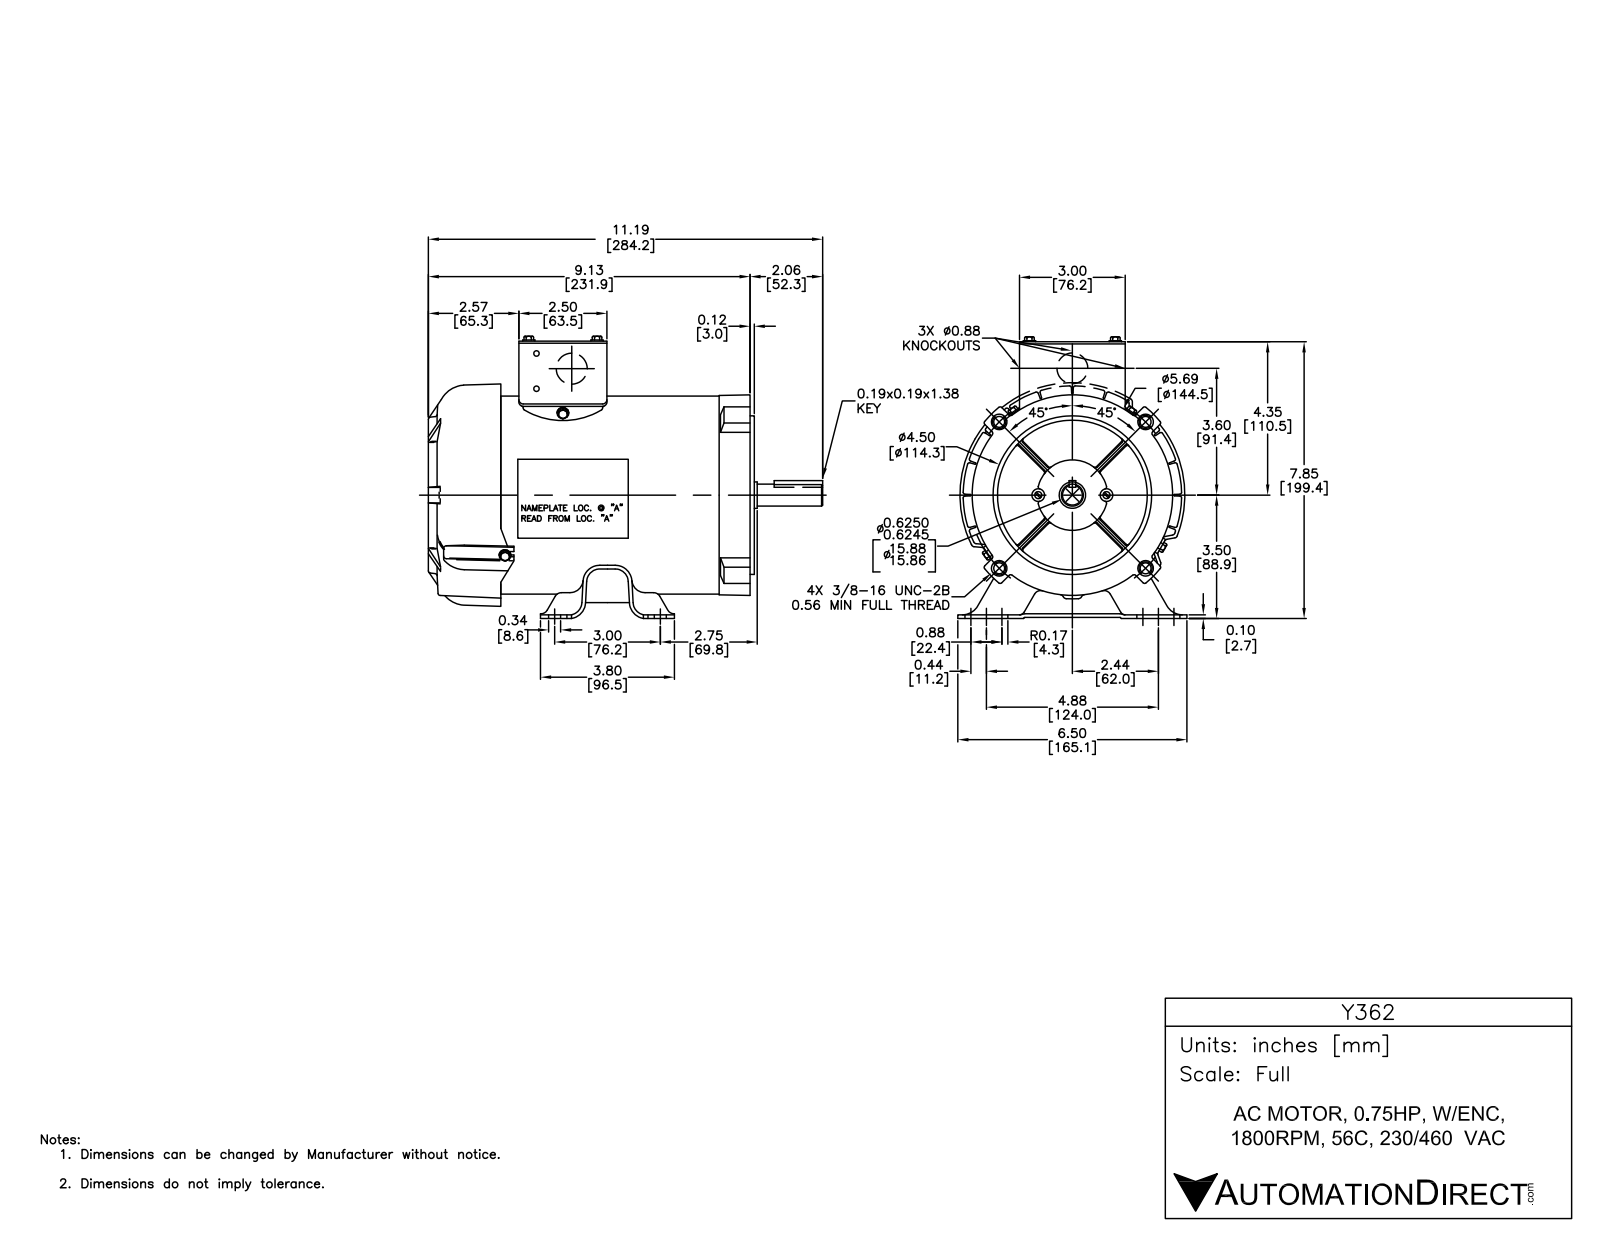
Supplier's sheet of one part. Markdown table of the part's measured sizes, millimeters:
| quantity | value |
| --- | --- |
| part name | SS75928-625_Rev05 R1 |
| STEP written by | SolidWorks 2017 (AUTOMOTIVE_DESIGN) |
| units | millimeters |
| bodies | 38 solids, 4415 faces (1176 planar, 916 cylindrical, 2323 other) |
| overall size | 282.6 × 207 × 165.1 |
| volume | 594 400 mm³ |
| surface area | 492 000 mm² |
| round holes (diameter × count) | 3.9 × 11, 5.6 × 10, 3.5 × 8, 4.8 × 5, 1.5 × 4, 3.4 × 4, 9.7 × 4, 22.4 × 3, 3.9 × 2, 4.2 × 2, 6 × 2, 7.1 × 2 |
| round bosses / shafts (diameter × count) | 4.2 × 11, 8.8 × 10, 23.1 × 3, 142.7 × 1, 139.6 × 1, 114.3 × 1, 50.8 × 1, 44.2 × 1 |
| partial cylindrical surfaces (radius × count) | 1.5 × 59, 1.3 × 41, 0.5 × 37, 0.8 × 28, 3.3 × 18, 2.3 × 16, 4.3 × 14, 6.4 × 14 |
| main face-to-face distances | 1.2, 2.6, 62.3, 75, 0.4, 192.9, 102.9, 90, 104.1, 88.8 |
| hole center spacings | 92, 99, 99, 53.8, 78.5, 9.5, 9.6, 48.4 |
